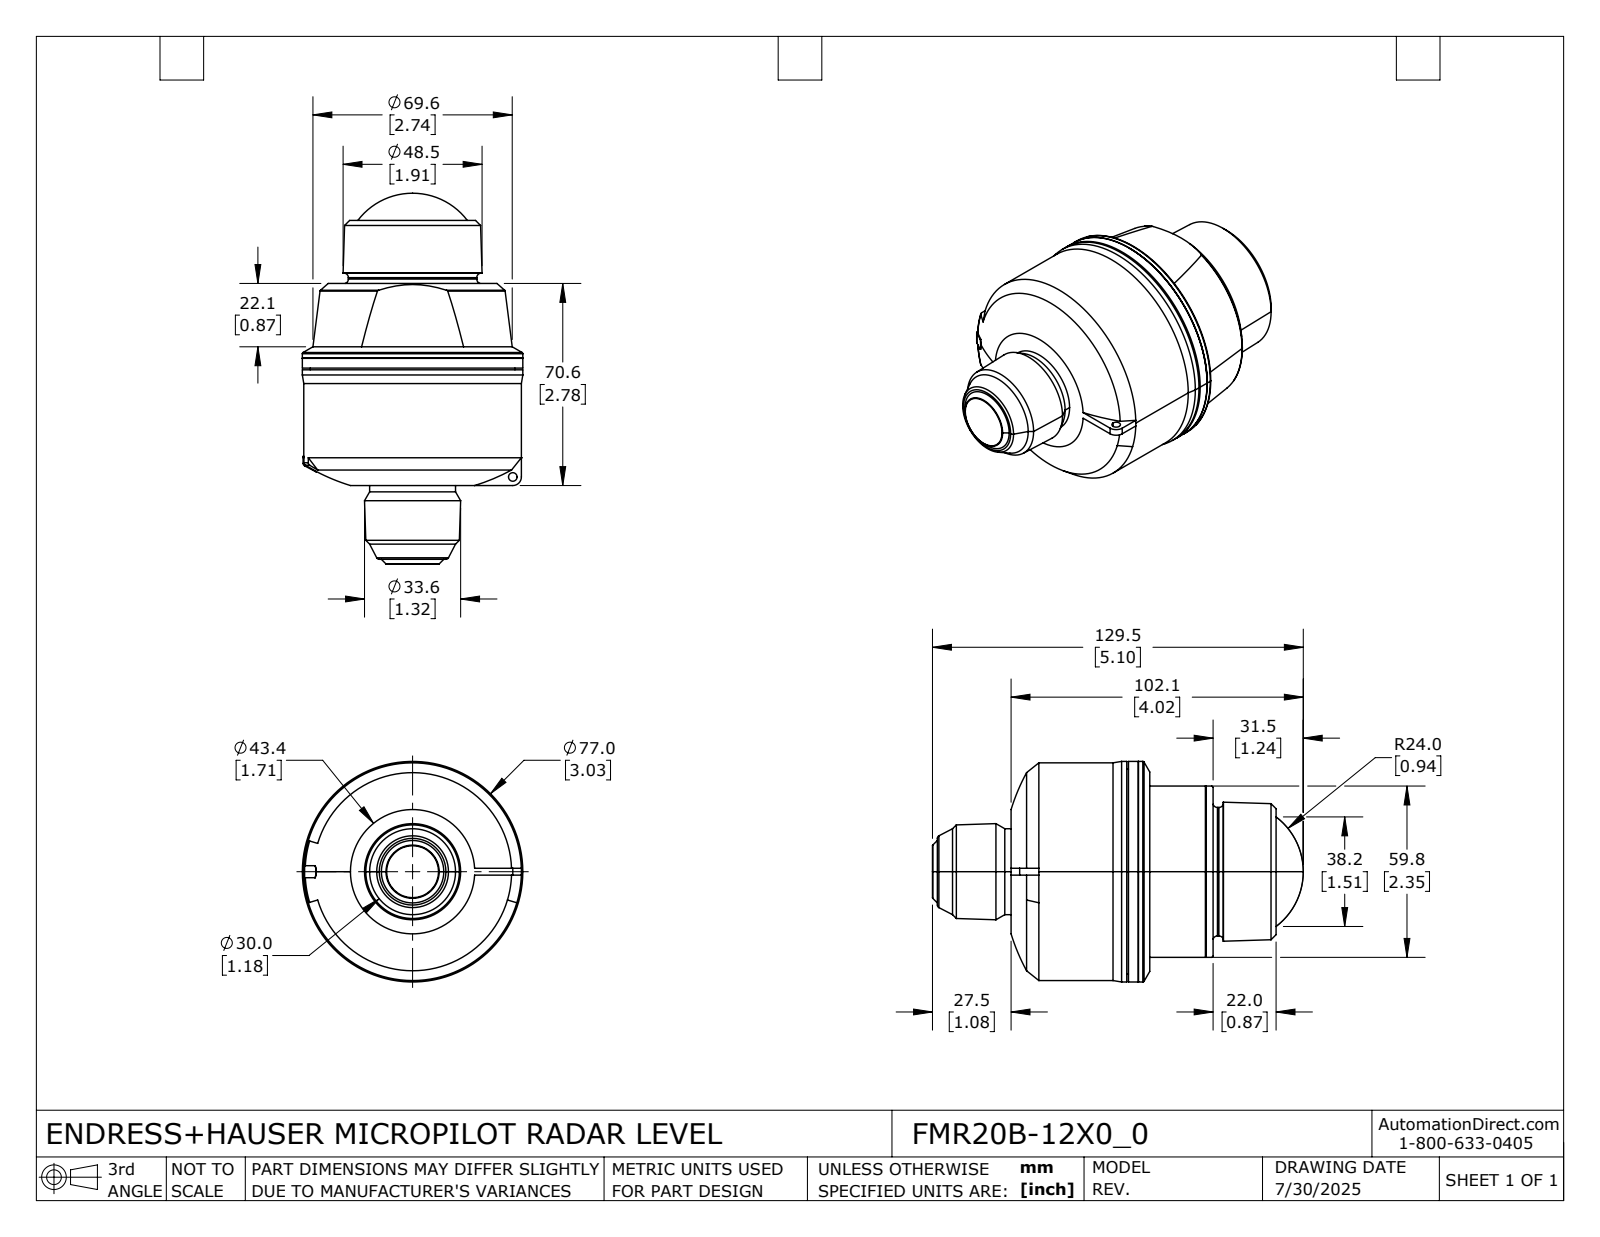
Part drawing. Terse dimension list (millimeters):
name: FMR20B-12X0_0
written by: SolidWorks 2024 (AUTOMOTIVE_DESIGN)
unit: mm
bodies: 1 solid, 100 faces (22 planar, 25 cylindrical, 53 other)
size: 129.5 × 77 × 77
volume: 347 200 mm³; area: 30 400 mm²
holes: 1× ⌀3
bosses: 1× ⌀77, 1× ⌀76, 1× ⌀71.5, 1× ⌀48.5, 1× ⌀44.9, 1× ⌀30
rounds: 2× R5, 1× R1, 1× R3
face distances: 70.6, 29.5, 30.1, 0.6, 41, 40.4, 59.8, 22, 51.6, 52.1
